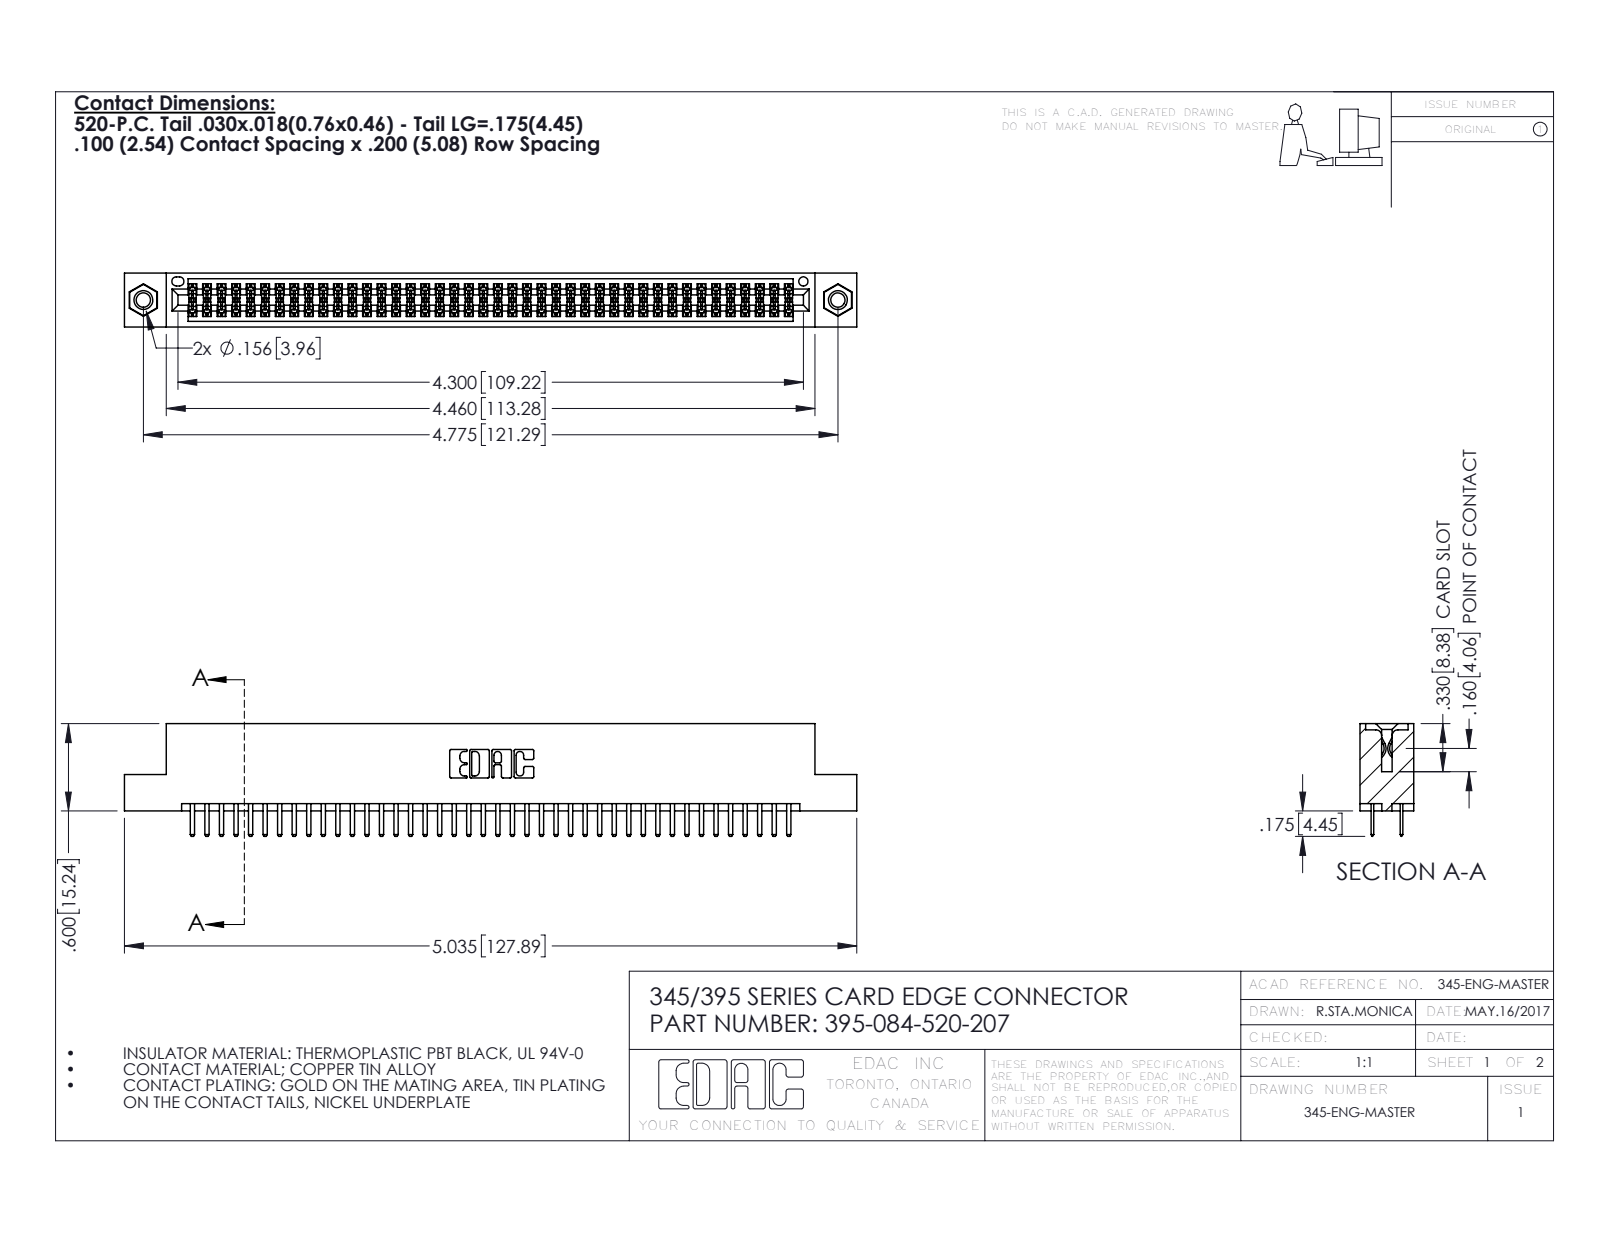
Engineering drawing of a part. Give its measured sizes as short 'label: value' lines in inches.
name: 345-292-001_345-293-120; 345-250-001_345-250-005-103; 345 Part_Flush Mounting Lugs - 0.156 Dia-TI; 395-084-520-207
written by: SolidWorks 2016 (CONFIG_CONTROL_DESIGN)
unit: in
bodies: 87 solids, 4722 faces (3052 planar, 1654 cylindrical, 16 other)
size: 5.035 × 0.775 × 0.37
volume: 0.755 in³; area: 28.27 in²
holes: 2× ⌀0.098, 2× ⌀0.125, 2× ⌀0.156, 1× ⌀0.064
bosses: 2× ⌀0.155
rounds: 126× R0.006, 88× R0.01, 22× R0.01, 6× R0.007, 6× R0.031, 3× R0.026, 2× R0.014, 2× R0.019
face distances: 0.072, 0.298, 0.2, 0.37, 0.098, 0.272, 0.025, 0.225, 0.022, 0.072
hole spacings: 0.27, 4.539, 4.775
